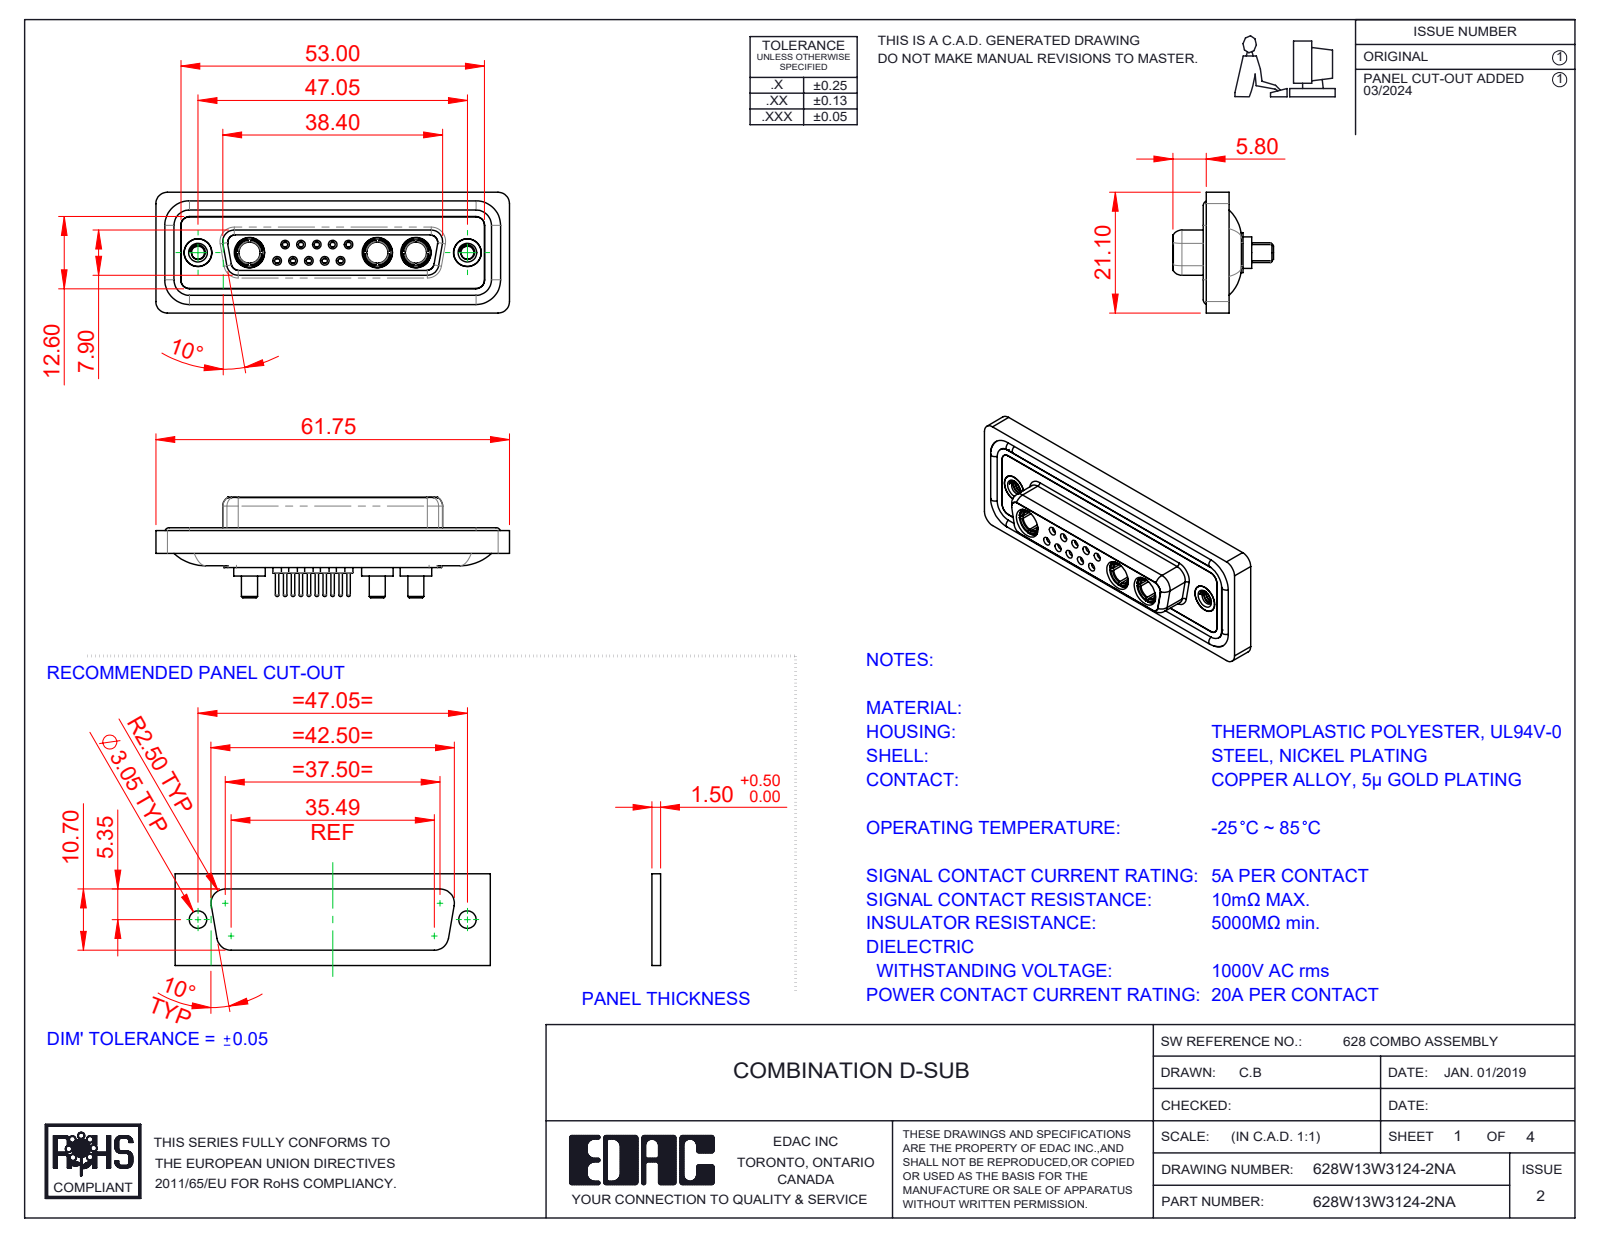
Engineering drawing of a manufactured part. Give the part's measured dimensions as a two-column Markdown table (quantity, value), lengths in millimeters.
| quantity | value |
| --- | --- |
| part name | 628Combo Waterproof Housing_25 Contacts; 628Combo Contact Row 1_24; 628Combo Housing_13W3; 628Combo Contact Row 2_24 (+5 more) |
| STEP written by | SolidWorks 2023 (CONFIG_CONTROL_DESIGN) |
| units | millimeters |
| bodies | 23 solids, 1156 faces (342 planar, 449 cylindrical, 365 other) |
| overall size | 61.75 × 21.1 × 17.55 |
| volume | 8 275 mm³ |
| surface area | 13 706 mm² |
| round holes (diameter × count) | 0.9 × 10, 1.1 × 10, 1.5 × 10, 2 × 10, 1.6 × 5, 1.7 × 5, 4.85 × 5, 3.7 × 3, 5.3 × 3, 2.26 × 2, 4 × 2, 4.05 × 2 |
| round bosses / shafts (diameter × count) | 2.2 × 10, 0.6 × 10, 1.6 × 9, 5.5 × 3, 5.2 × 3, 4.96 × 3, 4.75 × 3, 3.75 × 3 |
| partial cylindrical surfaces (radius × count) | 1.5 × 22, 2 × 18, 1.35 × 8, 1.6 × 8, 0.25 × 4, 0.5 × 4, 0.6 × 4, 0.65 × 4 |
| main face-to-face distances | 0.4, 1.8, 7.45, 5.65, 0.5, 6.6, 7.05, 1.6, 2.9, 1.1 |
| hole center spacings | 3.16, 2.77, 5.03, 5.04, 5.54, 8.31, 7.49, 2.76 |
